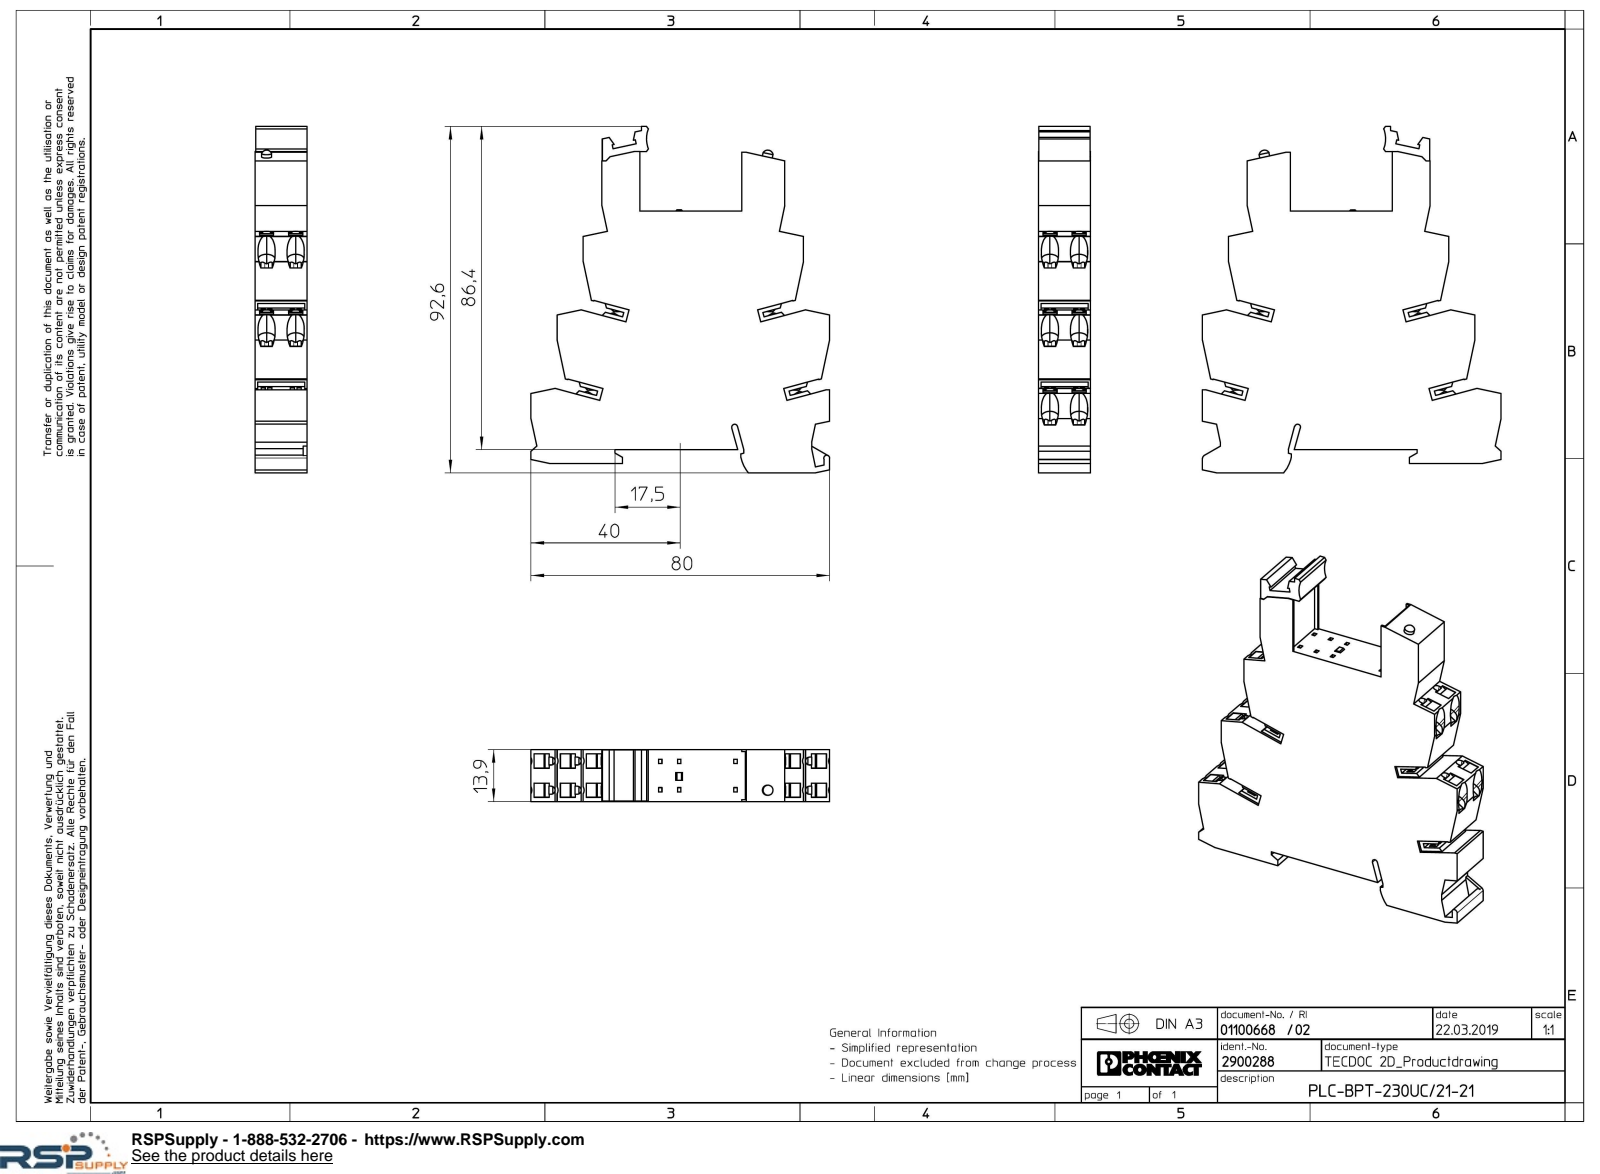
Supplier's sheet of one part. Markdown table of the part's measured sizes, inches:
| quantity | value |
| --- | --- |
| part name | PLC-BPT-14-ACT-SOC01-select |
| STEP written by | Creo Elements/Direct Modeling 20.1A 29-Sep-2018 (C) Parametric Technology GmbH (AUTOMOTIVE_DESIGN) |
| units | inches |
| bodies | 3 solids, 711 faces (613 planar, 74 cylindrical, 24 other) |
| overall size | 3.646 × 3.15 × 0.547 |
| volume | 3.851 in³ |
| surface area | 28.85 in² |
| partial cylindrical surfaces (radius × count) | 0.094 × 40, 0.039 × 20, 0.041 × 10, 0.031 × 2, 0.276 × 1, 0.374 × 1 |
| main face-to-face distances | 0.547, 0.041, 0.87, 2.512, 0.089, 0.146, 2.657, 0.441, 0.307, 0.098 |
